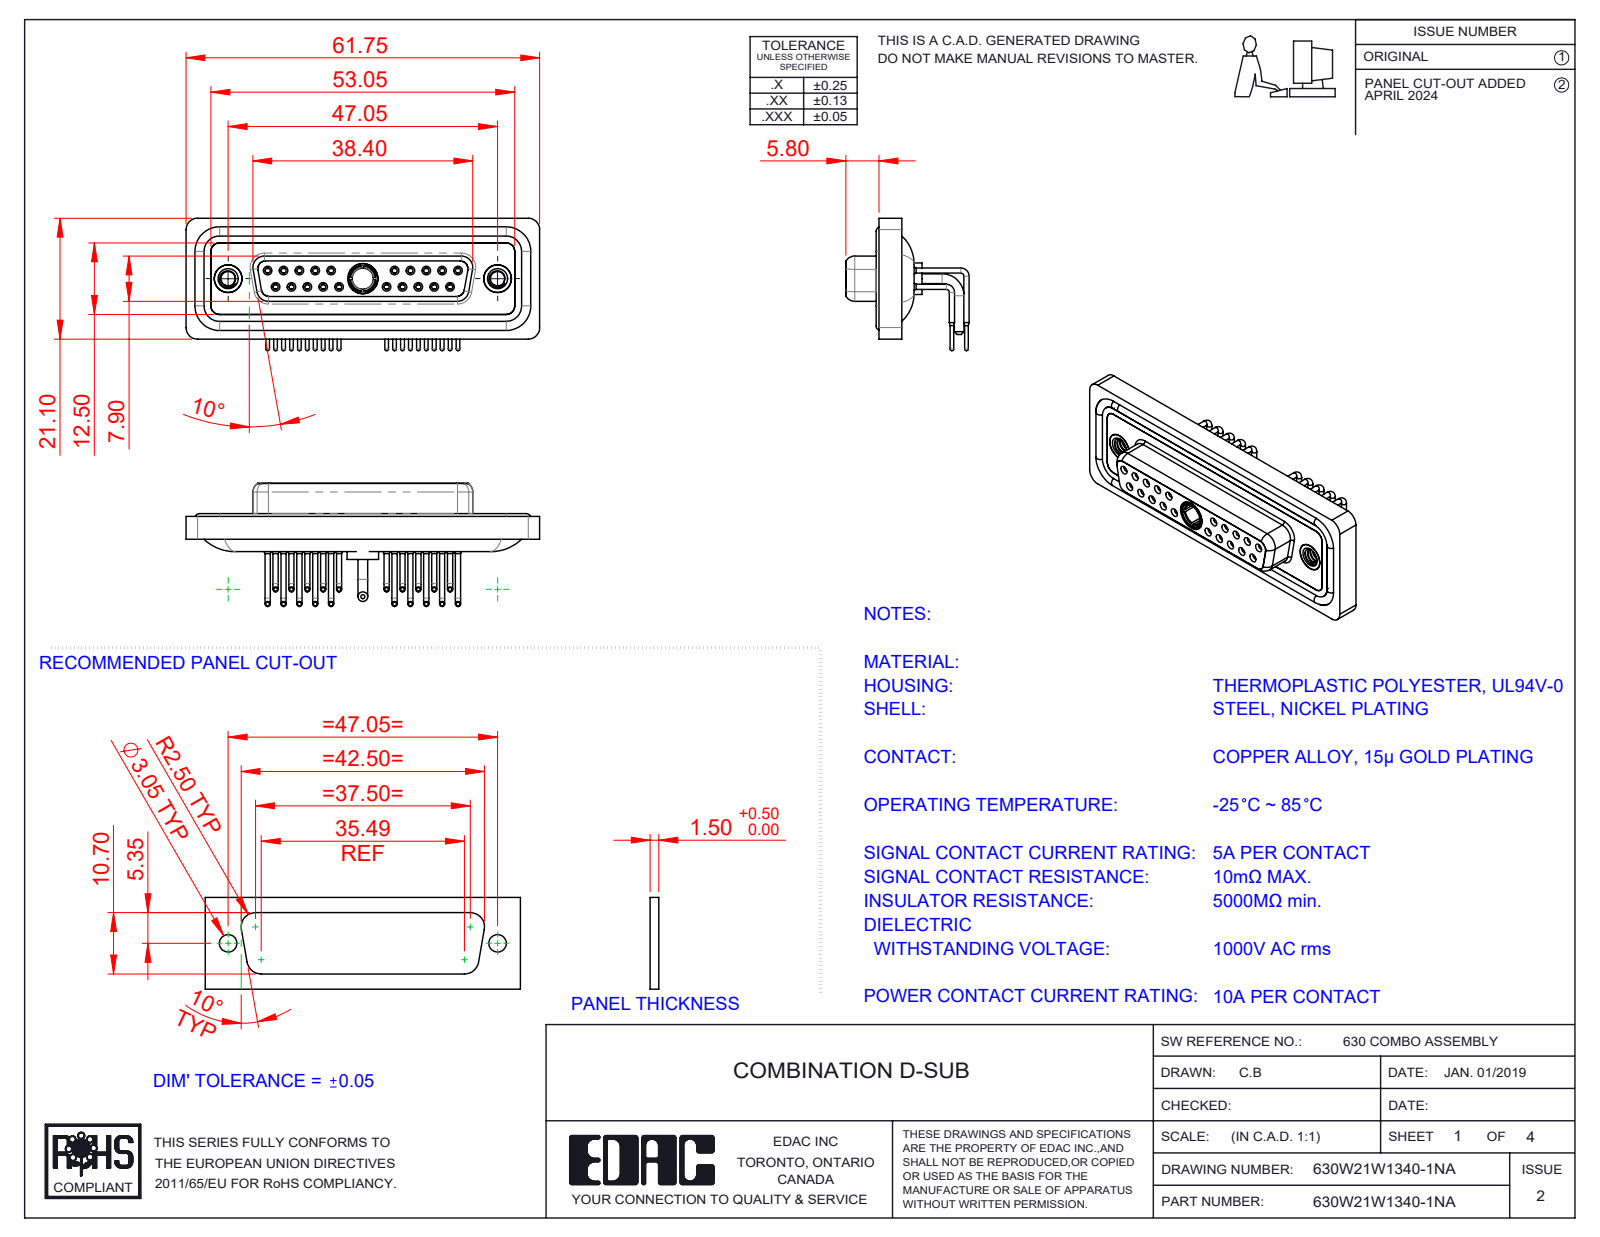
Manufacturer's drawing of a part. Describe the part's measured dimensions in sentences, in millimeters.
The part is named "630Combo Shell Rear_25 Contacts; 630Combo Contact Row 1_50 Contacts; 630Combo Contact Row 2_50 Contacts; 630Combo Housing_21W1 (+5 more)". Its 3-D file was written by "SolidWorks 2023 (CONFIG_CONTROL_DESIGN)". It is 29 solids with 1518 faces: 434 planar, 671 cylindrical and 413 other. Overall it measures 61.75 by 23.12 by 21.53 millimeters. Its volume is 8 440 cubic millimeters and its surface area 14 732 square millimeters. Round holes: 20 of diameter 0.9, 20 of diameter 1.1, 20 of diameter 1.5, 20 of diameter 2, 10 of diameter 1.6, 10 of diameter 1.7, 3 of diameter 4.85, 2 of diameter 2.5, 2 of diameter 4, 2 of diameter 4.05, 2 of diameter 5, 1 of diameter 3.7. Round bosses or shafts: 20 of diameter 0.9, 20 of diameter 0.65, 14 of diameter 1.6, 2 of diameter 4.95, 2 of diameter 4.8, 2 of diameter 1.7, 1 of diameter 5.5, 1 of diameter 5.2. Partial cylindrical surfaces (rounded edges, fillets, slot ends): 18 of radius 1.5, 18 of radius 2, 8 of radius 1.35, 8 of radius 1.6, 4 of radius 0.25, 4 of radius 0.5, 4 of radius 0.6, 4 of radius 0.65. The main face-to-face distances are 0.4, 1.8, 4.1, 1.6, 1.1, 2.5, 1.5, 3.1, 9.8, 0.45. The hole center spacings are 3.16, 2.77, 5.54, 8.31, 5.04, 19.39, 20.97, 22.16.
